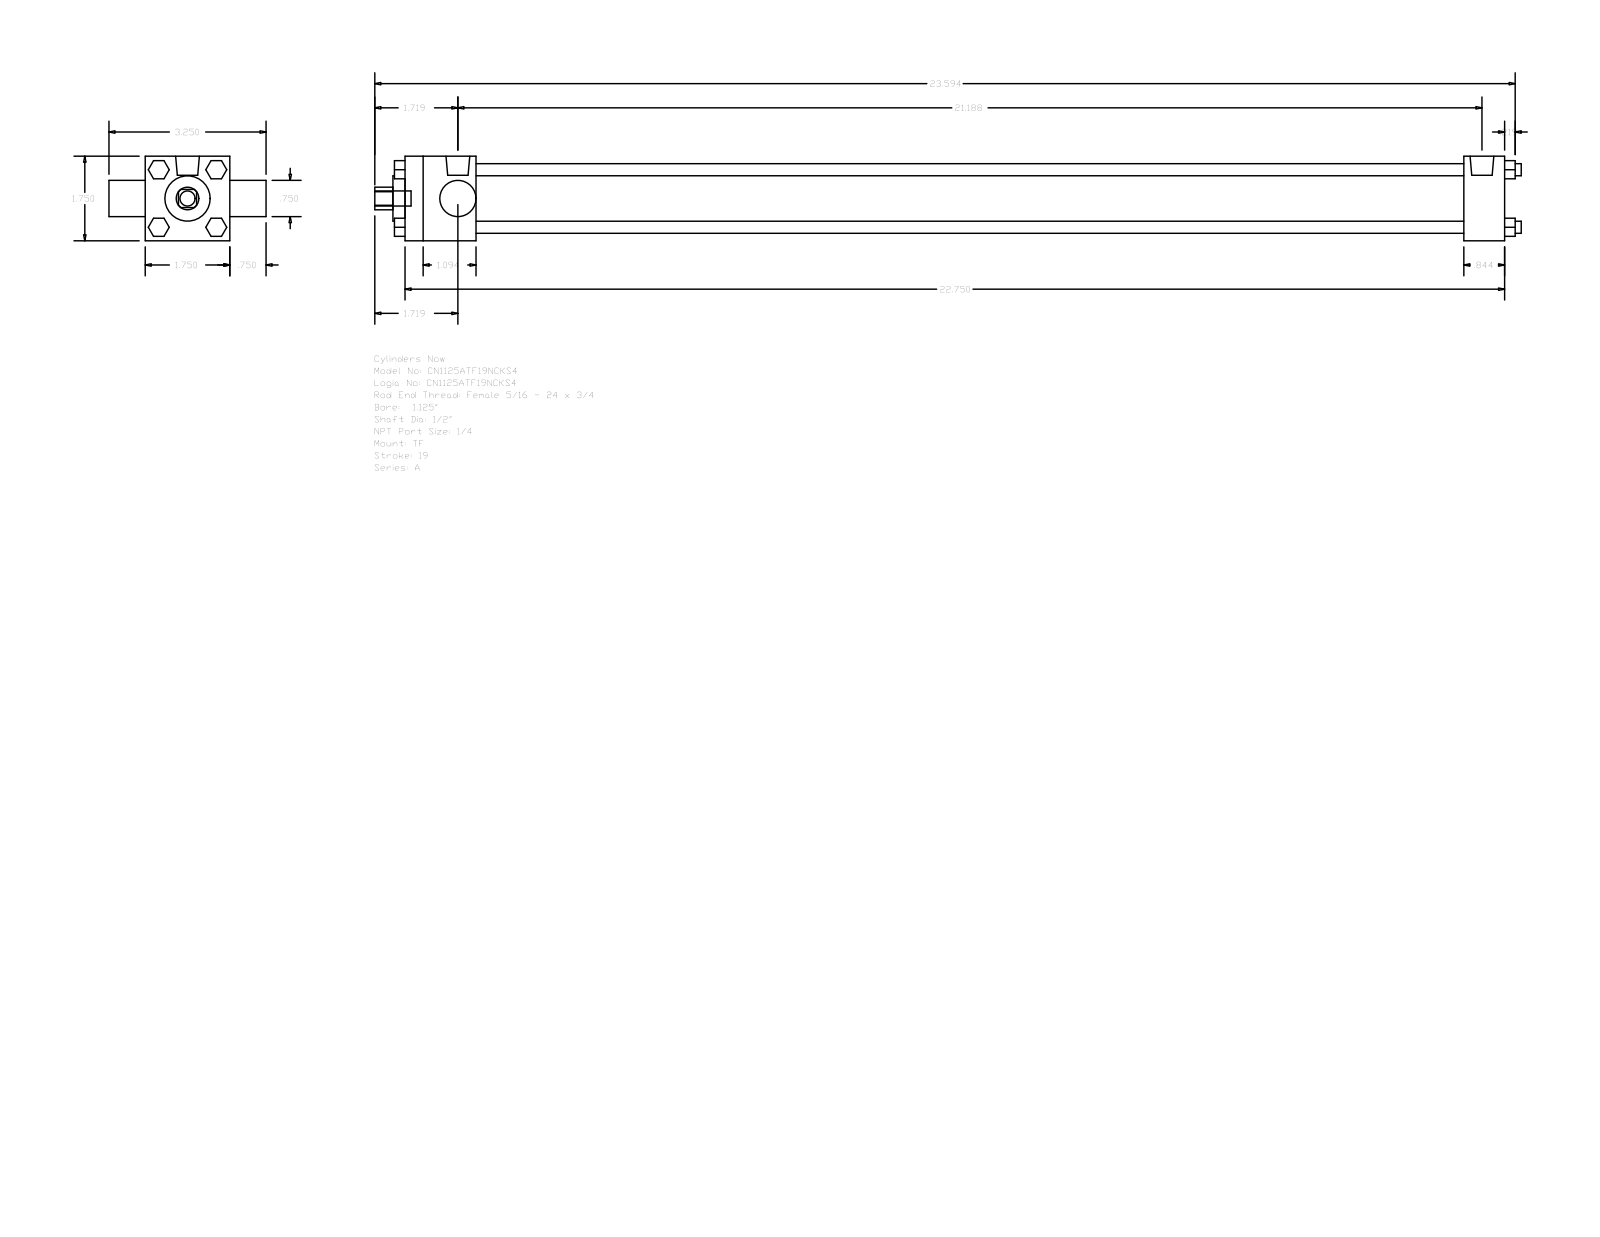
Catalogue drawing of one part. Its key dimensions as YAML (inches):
part_name: "A_TF__0112_0.5"
step_written_by: "GSSL Pune (CONFIG_CONTROL_DESIGN)"
units: inches
bodies: {solids: 0, faces: 120, planar: 92, cylindrical: 28, other: 0}
overall_size: [23.719, 3.25, 1.75]
round_holes:
  - {diameter: 0.5, count: 1}
  - {diameter: 0.75, count: 1}
  - {diameter: 0.937, count: 1}
  - {diameter: 1.255, count: 1}
round_bosses_or_shafts:
  - {diameter: 0.25, count: 4}
  - {diameter: 0.219, count: 3}
  - {diameter: 0.492, count: 2}
  - {diameter: 0.313, count: 1}
partial_cylinders:
  - {radius: 0.234, count: 1}
face_to_face_distances: [1.75, 22.75, 21.906, 0.844, 1.469, 20.437, 21.281, 0.75, 2.5, 0.375]
